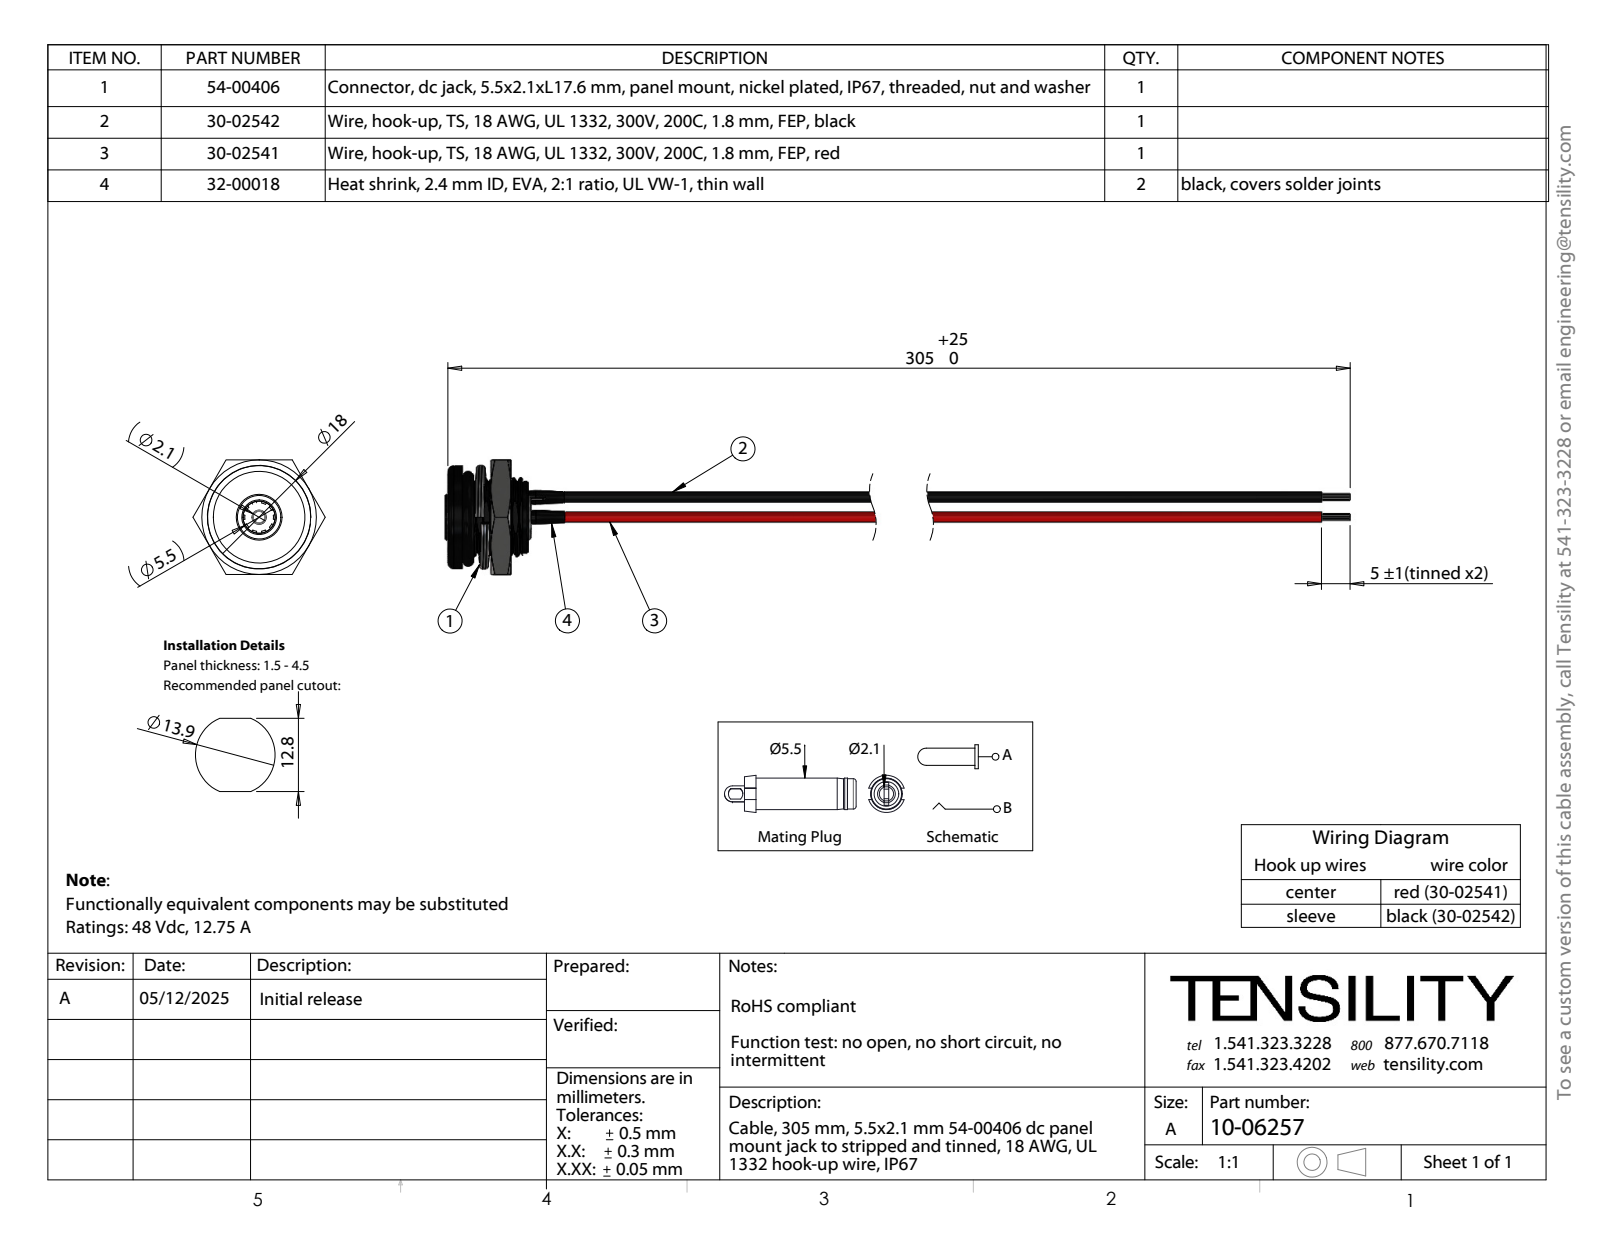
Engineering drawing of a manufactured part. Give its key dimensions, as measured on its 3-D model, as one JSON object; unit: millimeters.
{"part_name": "30-02542_stripped and tinned; 50-01012 center pin_Center pin; 50-01012; 50-01012 spring contact_Terminal (+8 more)", "step_written_by": "SolidWorks 2021 (CONFIG_CONTROL_DESIGN)", "units": "millimeters", "bodies": {"solids": 50, "faces": 537, "planar": 185, "cylindrical": 237, "other": 115}, "overall_size": [169.62, 23.09, 20], "volume_mm3": 3642, "surface_area_mm2": 14632, "round_holes": [[0.24, 38], [1.5, 2], [1.6, 1], [2.15, 1], [2.5, 1], [5.6, 1], [5.65, 1], [6.4, 1], [6.6, 1], [7.6, 1], [8, 1], [10, 1]], "round_bosses_or_shafts": [[1.8, 2], [18, 1], [12.6, 1], [12.59, 1], [7.3, 1], [6.2, 1], [2.1, 1]], "partial_cylinders_radius": [[0.5, 2], [3.35, 1], [6.9, 1]], "face_to_face_distances": [3.5, 7.51, 11.01, 2.5, 5.01, 8.51, 20, 8.5, 2, 1], "hole_center_spacings": [0.65, 0.43, 0.49, 0.42, 0.85, 0.88, 0.89, 0.73]}
